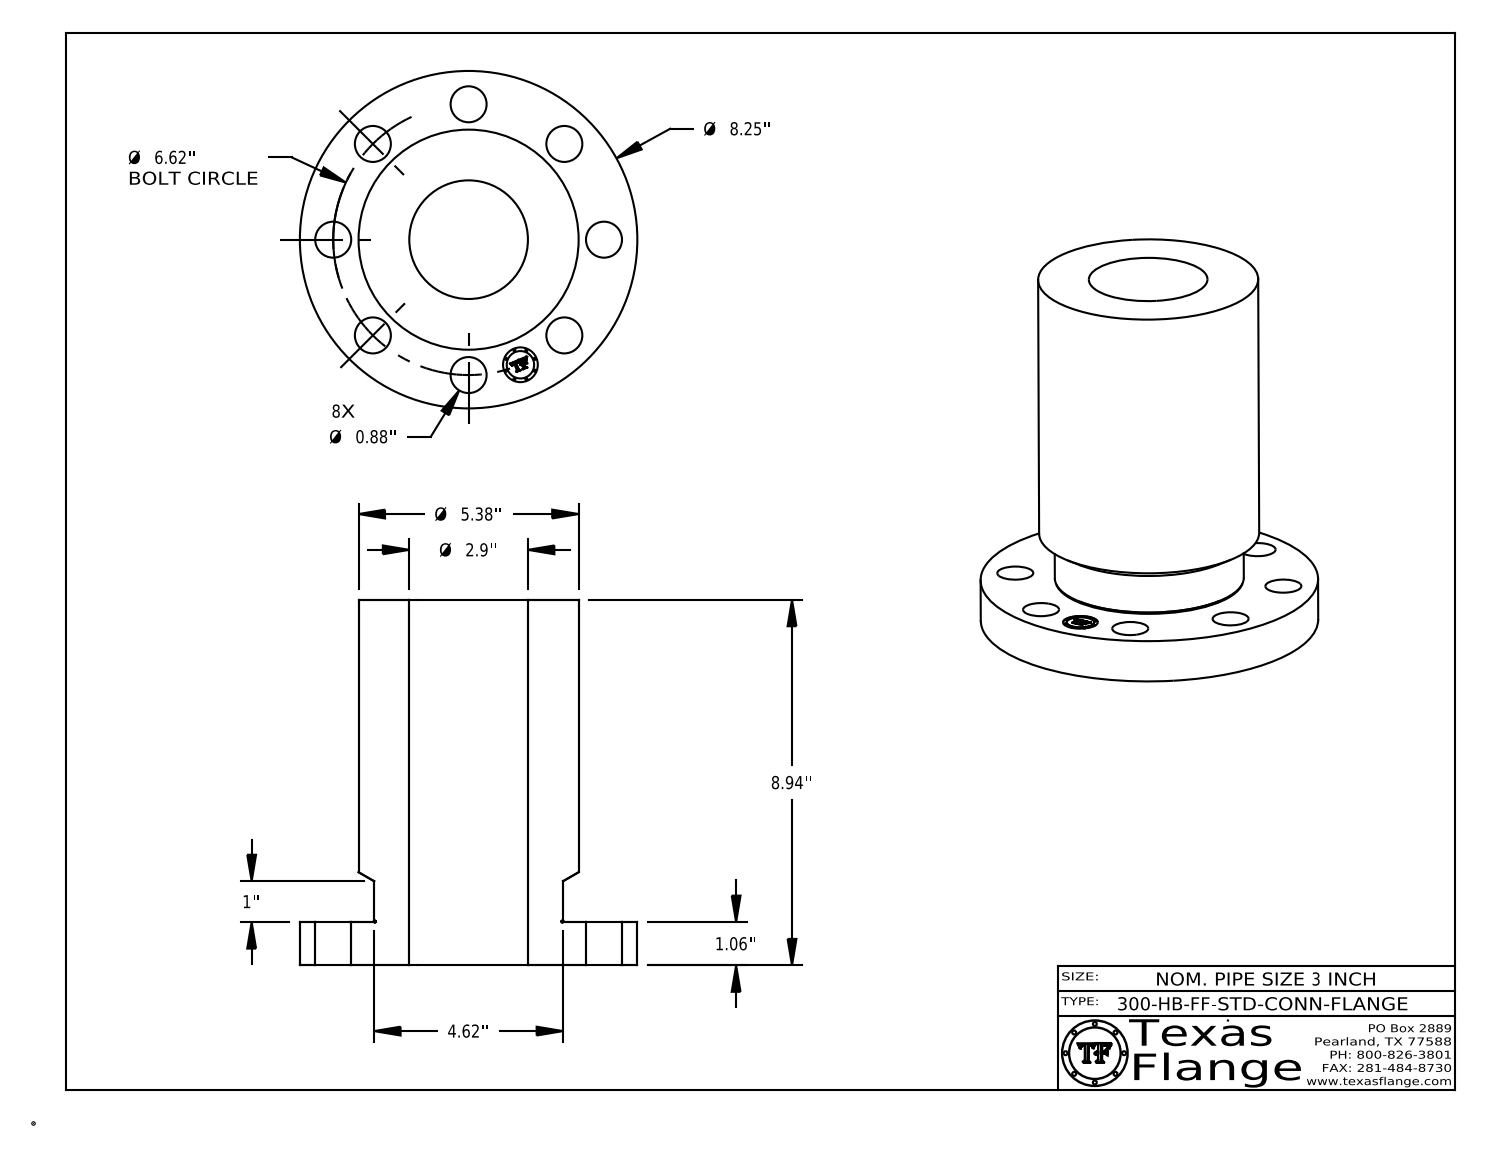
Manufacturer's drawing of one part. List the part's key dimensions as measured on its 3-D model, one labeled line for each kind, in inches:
Part name (STEP PRODUCT): 3-300-HB-FF-STD-CONN-FLANGE
STEP written by: CATIA V5 STEP AP214 (AUTOMOTIVE_DESIGN)
Units: inches
Bodies: 1 solid, 418 faces (368 planar, 44 cylindrical, 6 other)
Overall size (bounding box): 8.938 × 8.25 × 8.25
Volume: 164.8 in³ · Surface area: 356.8 in²
Round holes (diameter × count): ⌀0.88 ×8, ⌀0.85 ×1, ⌀2.9 ×1
Round bosses / shafts (diameter × count): ⌀0.051 ×8, ⌀8.25 ×1, ⌀5.38 ×1, ⌀4.62 ×1, ⌀0.67 ×1
Main face-to-face distances: 1.057, 8.937, 7.88, 1.052, 7.885, 0.016, 0.254, 0.249, 0.046, 0.165
Hole centre spacings: 3.31, 2.533, 6.116, 4.681, 4.681, 1.291, 3.678, 6.493
